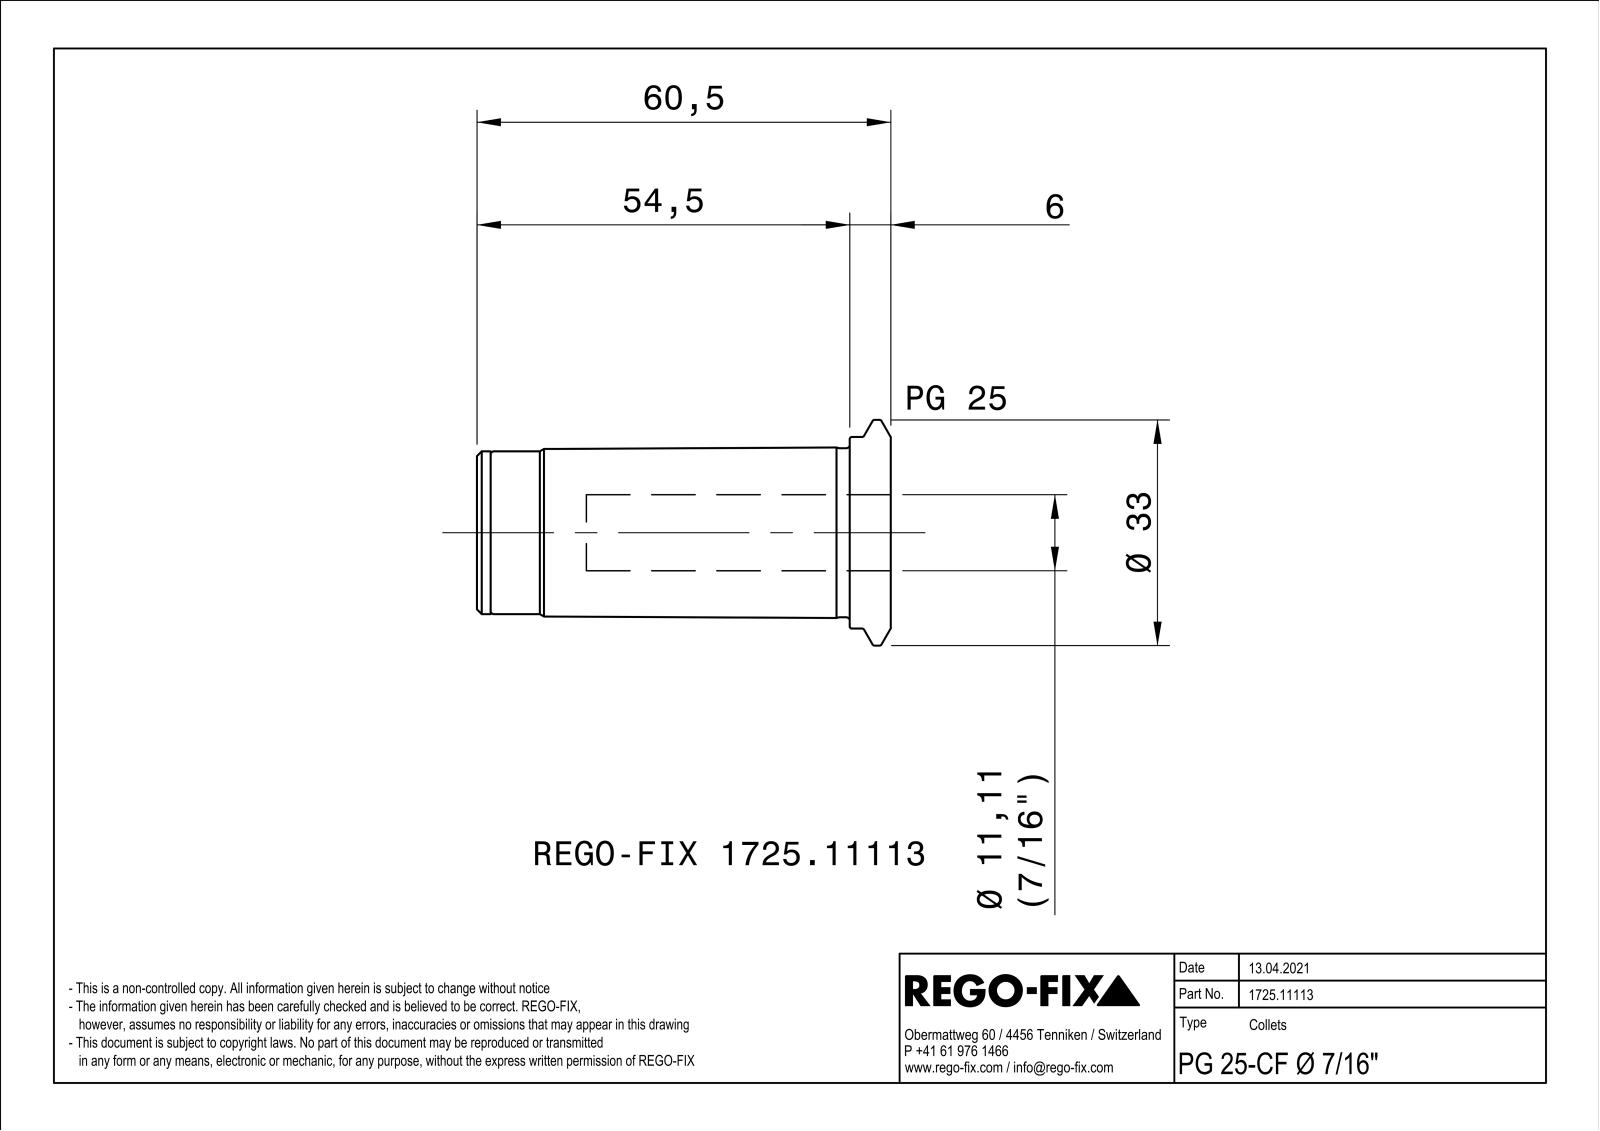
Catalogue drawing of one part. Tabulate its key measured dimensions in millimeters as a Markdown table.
| quantity | value |
| --- | --- |
| part name | NOCUT |
| STEP written by | SIEMENS PLM Software Solid Edge ST10 (AUTOMOTIVE_DESIGN) |
| units | millimeters |
| bodies | 1 solid, 89 faces (23 planar, 27 cylindrical, 39 other) |
| overall size | 60.5 × 33 × 32.99 |
| volume | 22 906 mm³ |
| surface area | 11 172 mm² |
| round holes (diameter × count) | 2.5 × 3, 5.2 × 1, 6.92 × 1, 8.2 × 1, 11.11 × 1, 20.92 × 1, 22.2 × 1 |
| round bosses / shafts (diameter × count) | 33 × 1, 28 × 1, 24.7 × 1, 23.8 × 1, 20.4 × 1, 12 × 1 |
| partial cylindrical surfaces (radius × count) | 0.75 × 3 |
| main face-to-face distances | 1, 60.5, 52.6, 7.9, 58.5, 5.9, 2, 50, 2.6, 8.5 |
| hole center spacings | 7.75, 13.43, 13.42 |
